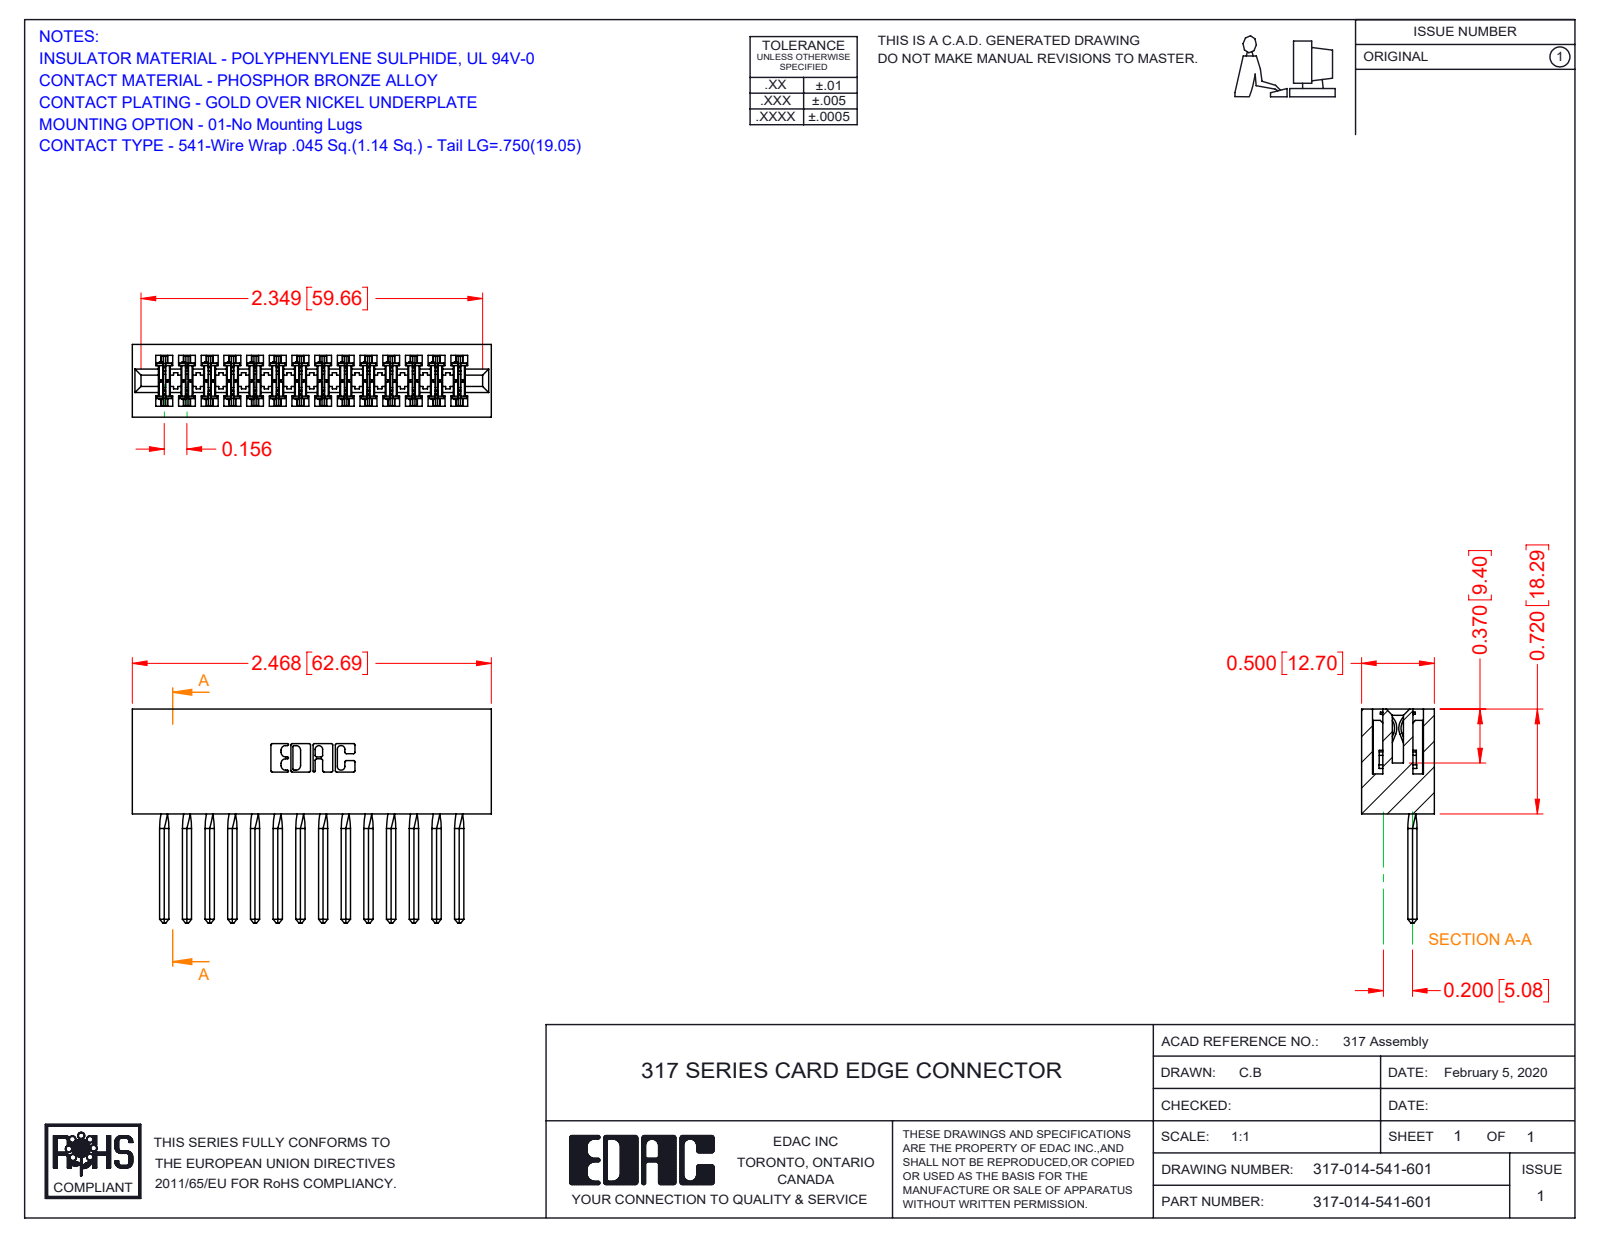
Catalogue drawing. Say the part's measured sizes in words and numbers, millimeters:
The part is named "317-014-541-601; 317-290-002_541; 317 Part_Lugless". Its 3-D file was written by "SolidWorks 2016 (CONFIG_CONTROL_DESIGN)". It is 15 solids with 2218 faces: 1786 planar, 376 cylindrical and 56 other. Overall it measures 62.7 by 37.3 by 12.7 millimeters. Its volume is 11 000 cubic millimeters and its surface area 14 820 square millimeters. Partial cylindrical surfaces (rounded edges, fillets, slot ends): 28 of radius 0.4, 22 of radius 0.3, 6 of radius 0.2, 6 of radius 0.8, 3 of radius 0.7, 2 of radius 2.4, 2 of radius 2.5, 2 of radius 2.8. The main face-to-face distances are 12.7, 1.9, 10.8, 2.8, 5.6, 8.9, 1.7, 4, 5, 8.4.
